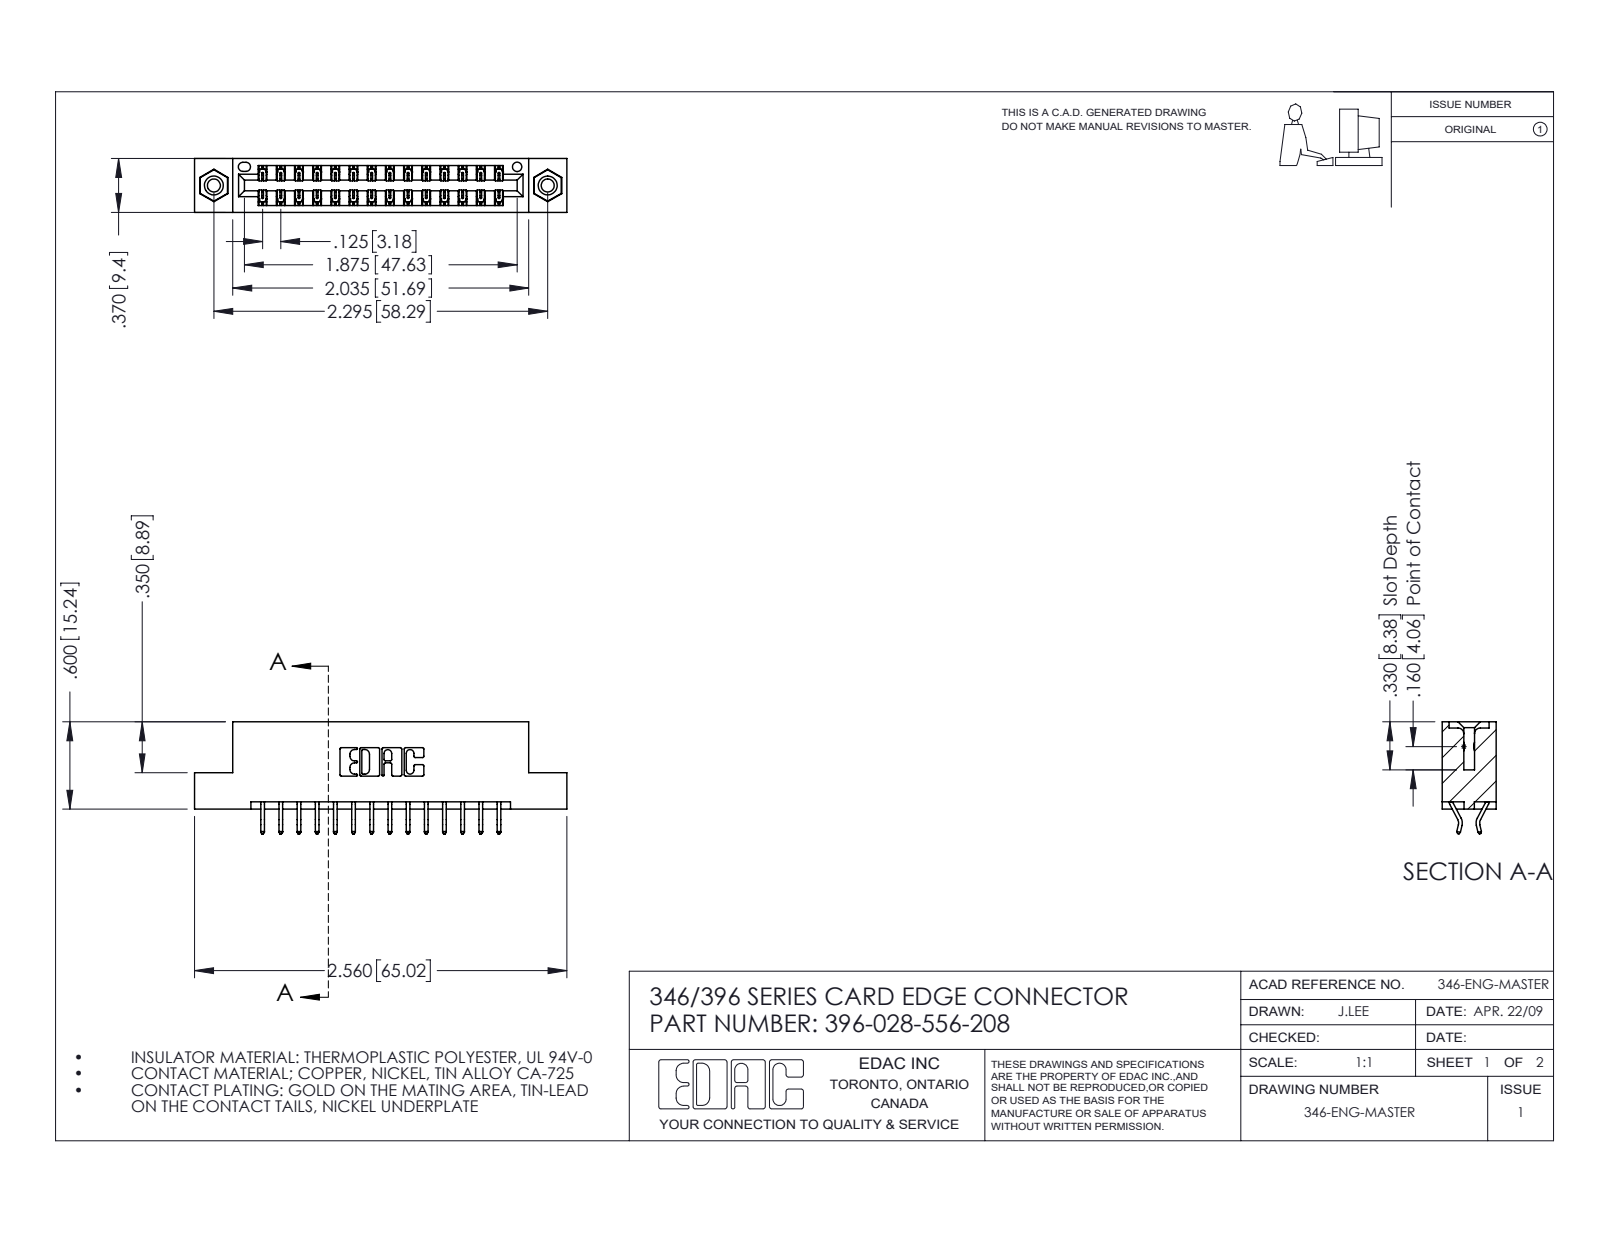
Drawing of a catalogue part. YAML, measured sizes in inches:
part_name: "396-028-556-208; 345-250-001_345-250-003-102; 345-292-001_556 Tail; 346 Part_Flush Mounting Lugs - 0.156 Dia-TI"
step_written_by: "SolidWorks 2016 (CONFIG_CONTROL_DESIGN)"
units: inches
bodies: {solids: 31, faces: 1806, planar: 1200, cylindrical: 590, other: 16}
overall_size: [2.56, 0.77, 0.37]
volume: 0.373
surface_area: 12.34
round_holes:
  - {diameter: 0.089, count: 2}
  - {diameter: 0.125, count: 2}
  - {diameter: 0.156, count: 2}
  - {diameter: 0.064, count: 1}
round_bosses_or_shafts:
  - {diameter: 0.155, count: 2}
partial_cylinders:
  - {radius: 0.006, count: 42}
  - {radius: 0.01, count: 22}
  - {radius: 0.007, count: 6}
  - {radius: 0.031, count: 6}
  - {radius: 0.026, count: 3}
  - {radius: 0.01, count: 2}
  - {radius: 0.014, count: 2}
  - {radius: 0.022, count: 2}
face_to_face_distances: [0.048, 0.322, 0.25, 0.37, 0.025, 0.072, 0.298, 0.275, 0.148, 0.222]
hole_center_spacings: [0.246, 2.089, 2.295]
